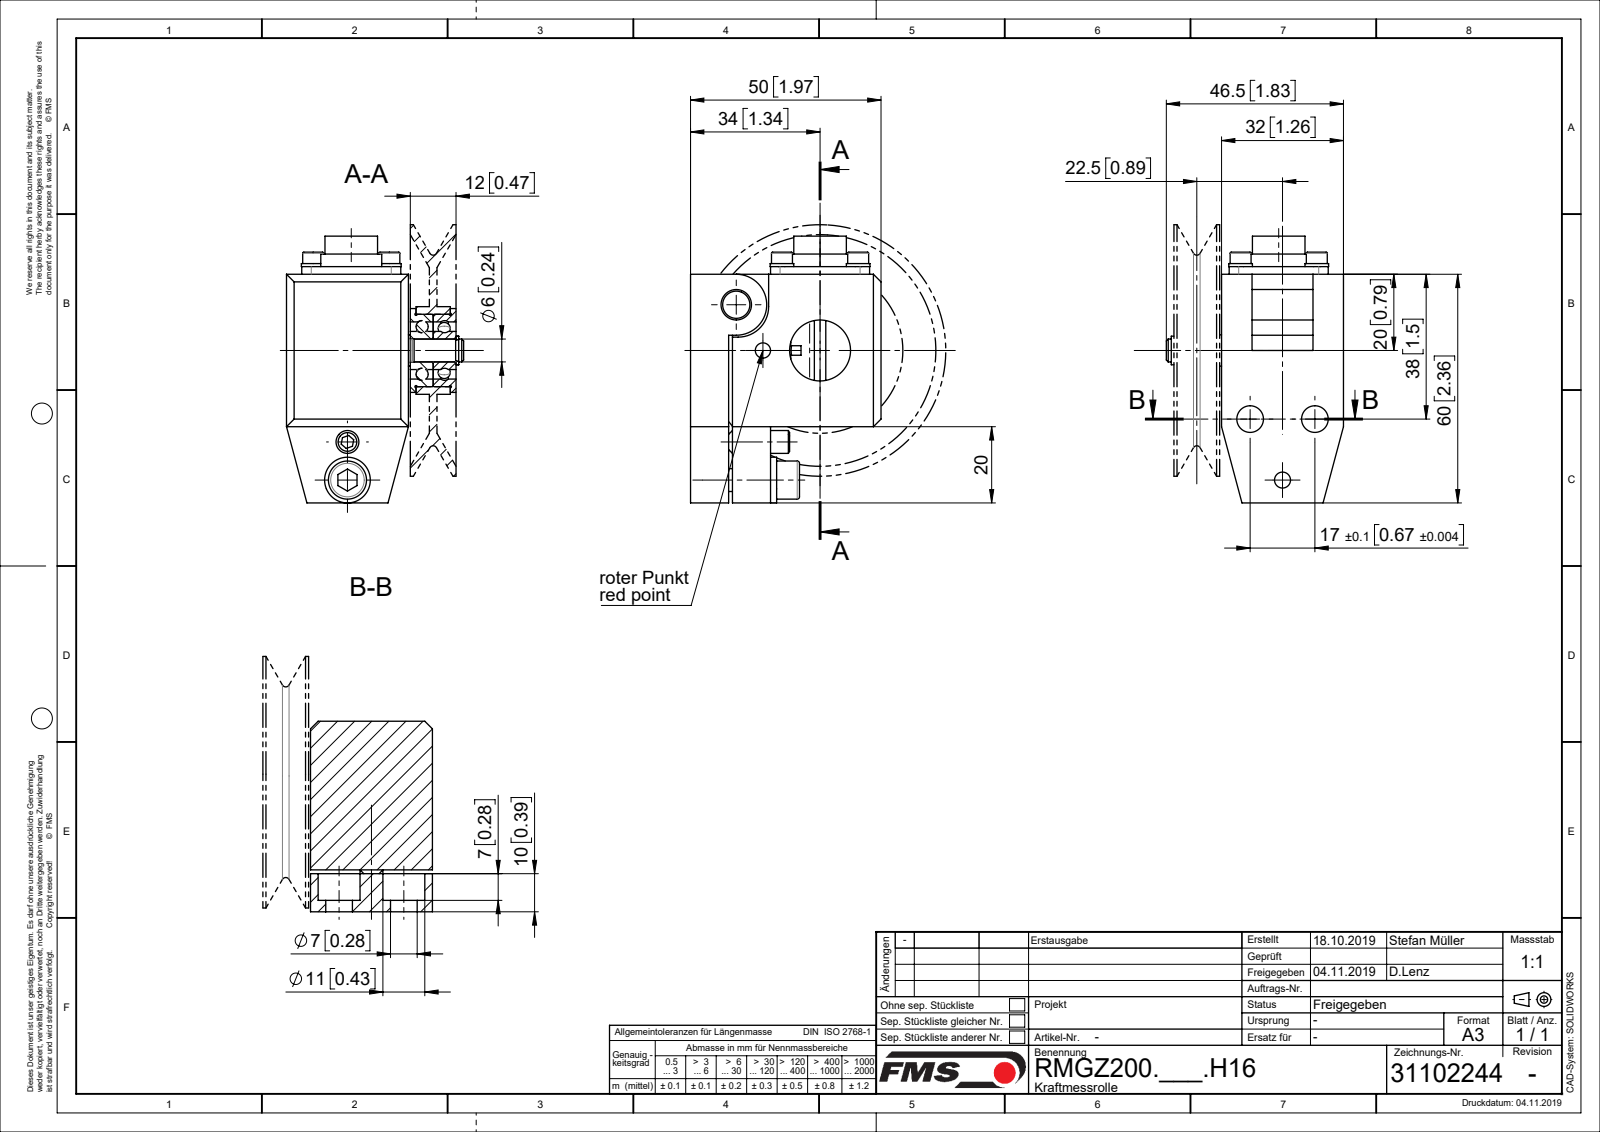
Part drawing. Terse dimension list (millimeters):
name: R1302201; R1206234; R1301296; R1302202 (+8 more)
written by: Mechanical Desktop 2009 (CONFIG_CONTROL_DESIGN)
unit: mm
bodies: 20 solids, 449 faces (136 planar, 184 cylindrical, 129 other)
size: 73 × 67 × 46.5
volume: 81 976 mm³; area: 42 349 mm²
holes: 4× ⌀2.6, 4× ⌀3.2, 2× ⌀6, 2× ⌀7, 2× ⌀11, 2× ⌀15, 1× ⌀0.5, 1× ⌀4, 1× ⌀4.33, 1× ⌀5.15, 1× ⌀5.3, 1× ⌀5.7
bosses: 5× ⌀1.5, 4× ⌀6.2, 4× ⌀5.5, 4× ⌀3, 2× ⌀10, 1× ⌀66, 1× ⌀23, 1× ⌀22
rounds: 4× R2.5, 2× R8
face distances: 10, 11, 2, 40, 5, 1, 7, 32, 8, 5.5
hole spacings: 14.14, 20, 10.4, 18.12, 28.28, 10, 13.89, 15
